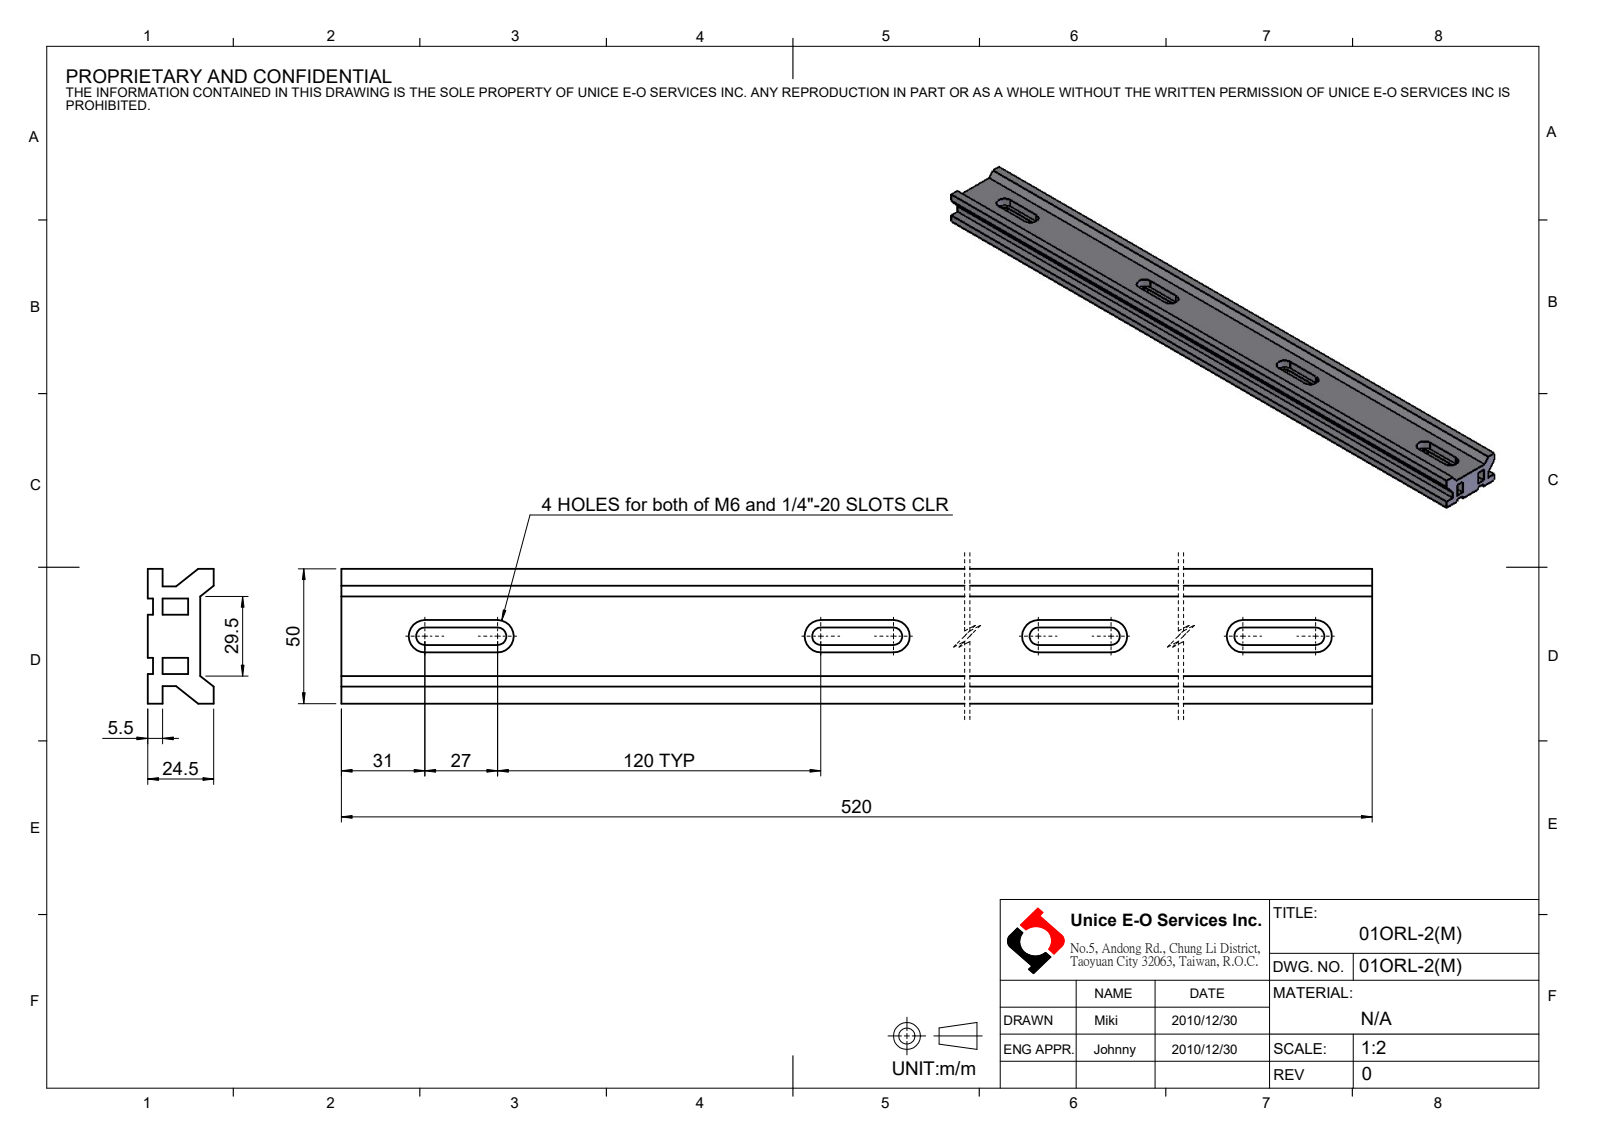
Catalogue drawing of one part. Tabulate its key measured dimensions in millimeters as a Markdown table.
| quantity | value |
| --- | --- |
| part name | 01ORL-2(M) |
| STEP written by | SolidWorks 2016 (CONFIG_CONTROL_DESIGN) |
| units | millimeters |
| bodies | 1 solid, 86 faces (54 planar, 28 cylindrical, 4 other) |
| overall size | 520 × 50 × 24.5 |
| volume | 394 102 mm³ |
| surface area | 132 074 mm² |
| round holes (diameter × count) | 5 × 2 |
| partial cylindrical surfaces (radius × count) | 3.25 × 8, 6 × 8 |
| main face-to-face distances | 14, 19.5, 5.5, 6, 11, 9.5, 22, 17, 33, 39 |
| hole center spacings | 500 |
